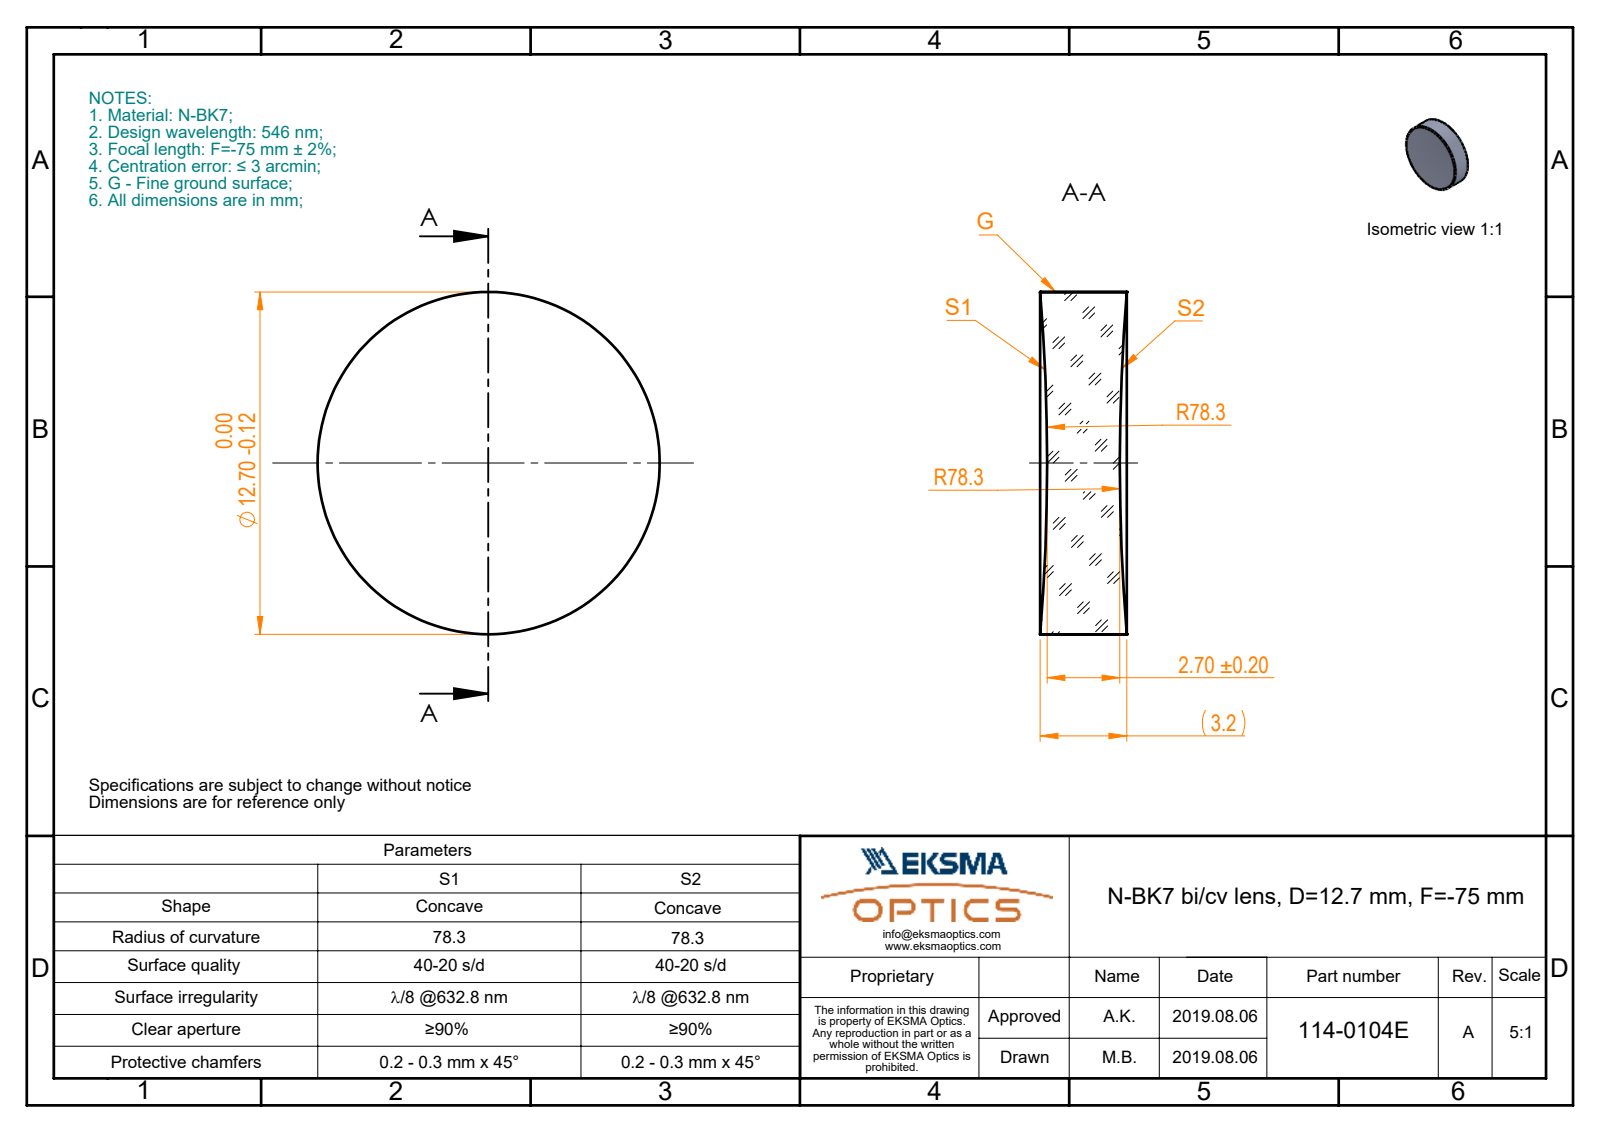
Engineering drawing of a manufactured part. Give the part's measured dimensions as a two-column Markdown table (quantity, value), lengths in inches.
| quantity | value |
| --- | --- |
| part name | 114-0114E BK7 bi-cv 12.7 F-75 |
| STEP written by | SolidWorks 2017 (CONFIG_CONTROL_DESIGN) |
| units | inches |
| bodies | 1 solid, 6 faces (0 planar, 2 cylindrical, 4 other) |
| overall size | 0.5 × 0.5 × 0.127 |
| volume | 0.023 in³ |
| surface area | 0.592 in² |
| round bosses / shafts (diameter × count) | 0.5 × 1 |
